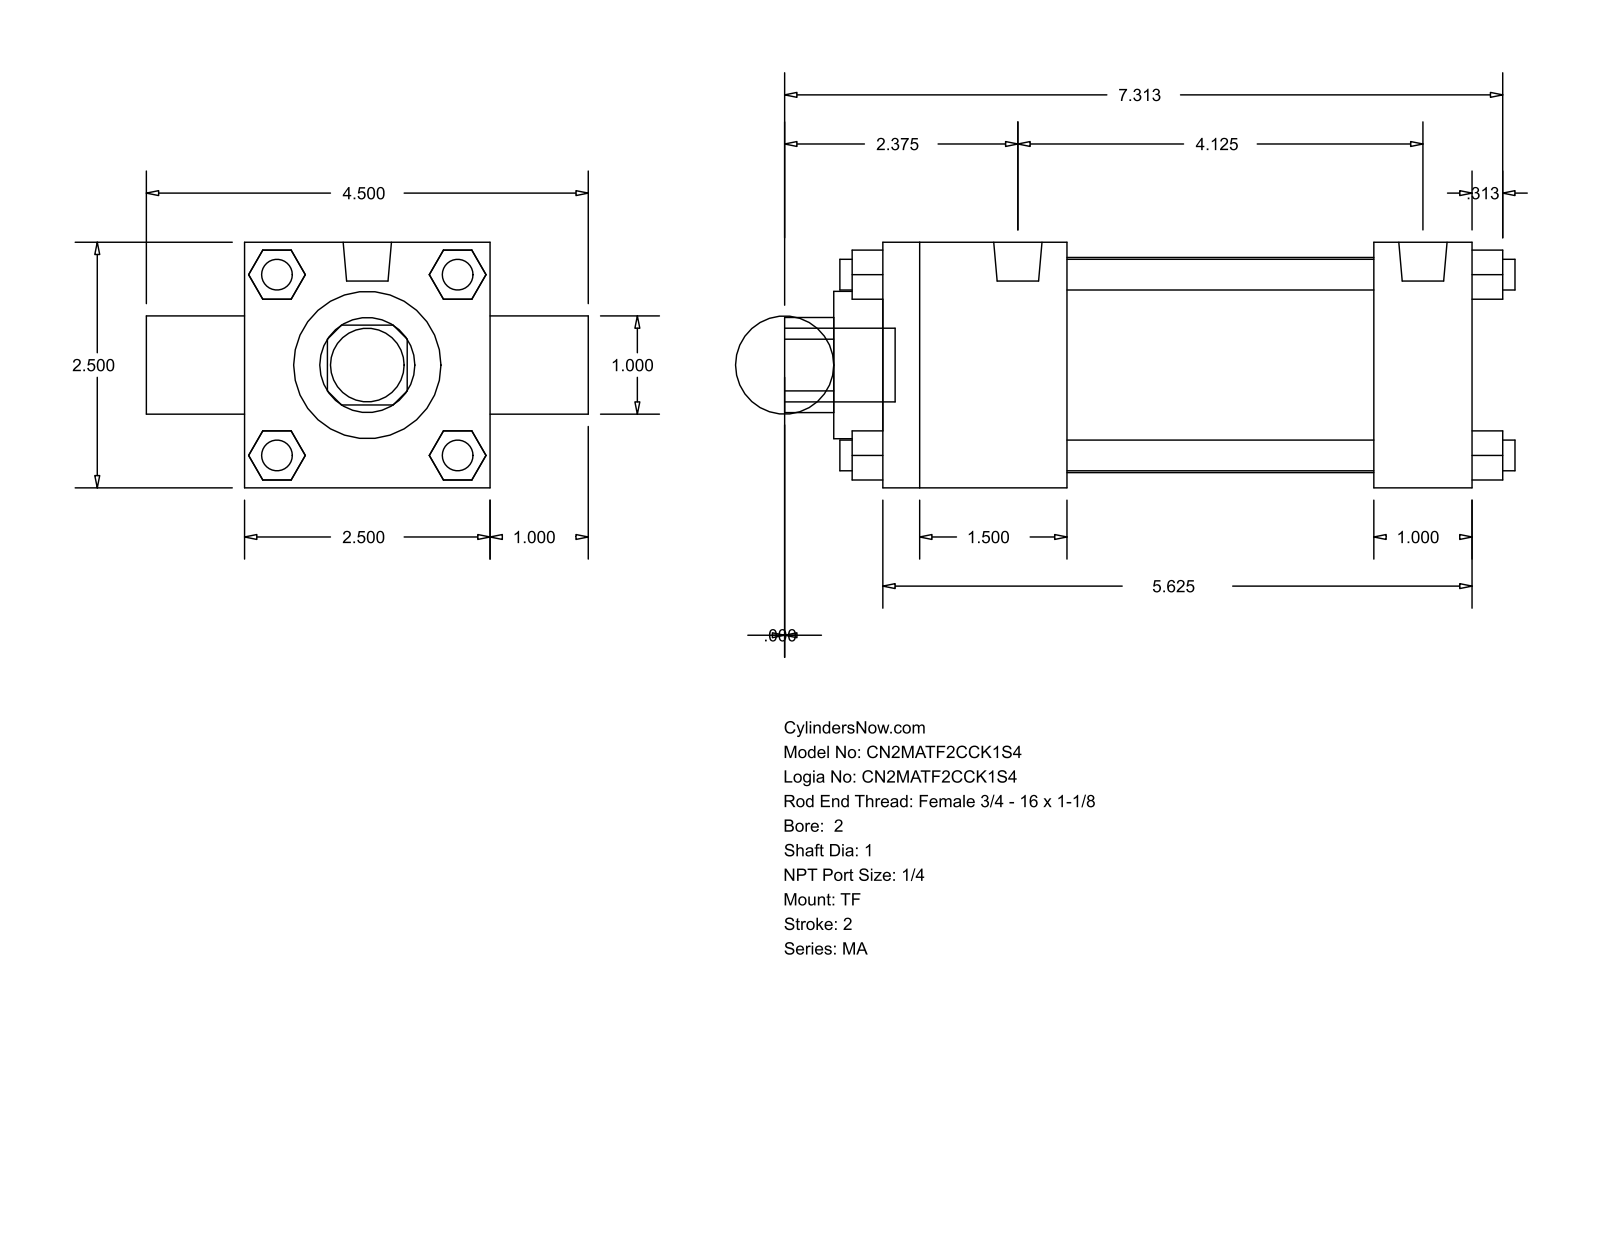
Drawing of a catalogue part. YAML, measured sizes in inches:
part_name: "MA_TF__0200_1"
step_written_by: "GSSL Pune (CONFIG_CONTROL_DESIGN)"
units: inches
bodies: {solids: 0, faces: 120, planar: 92, cylindrical: 28, other: 0}
overall_size: [7.437, 4.5, 2.5]
round_holes:
  - {diameter: 1, count: 2}
  - {diameter: 1.5, count: 1}
  - {diameter: 2.19, count: 1}
round_bosses_or_shafts:
  - {diameter: 0.313, count: 7}
  - {diameter: 0.492, count: 2}
  - {diameter: 0.75, count: 1}
partial_cylinders:
  - {radius: 0.484, count: 1}
face_to_face_distances: [2.5, 1, 6, 0.5, 1.875, 5, 3.125, 4.125, 3.5, 1.593]
